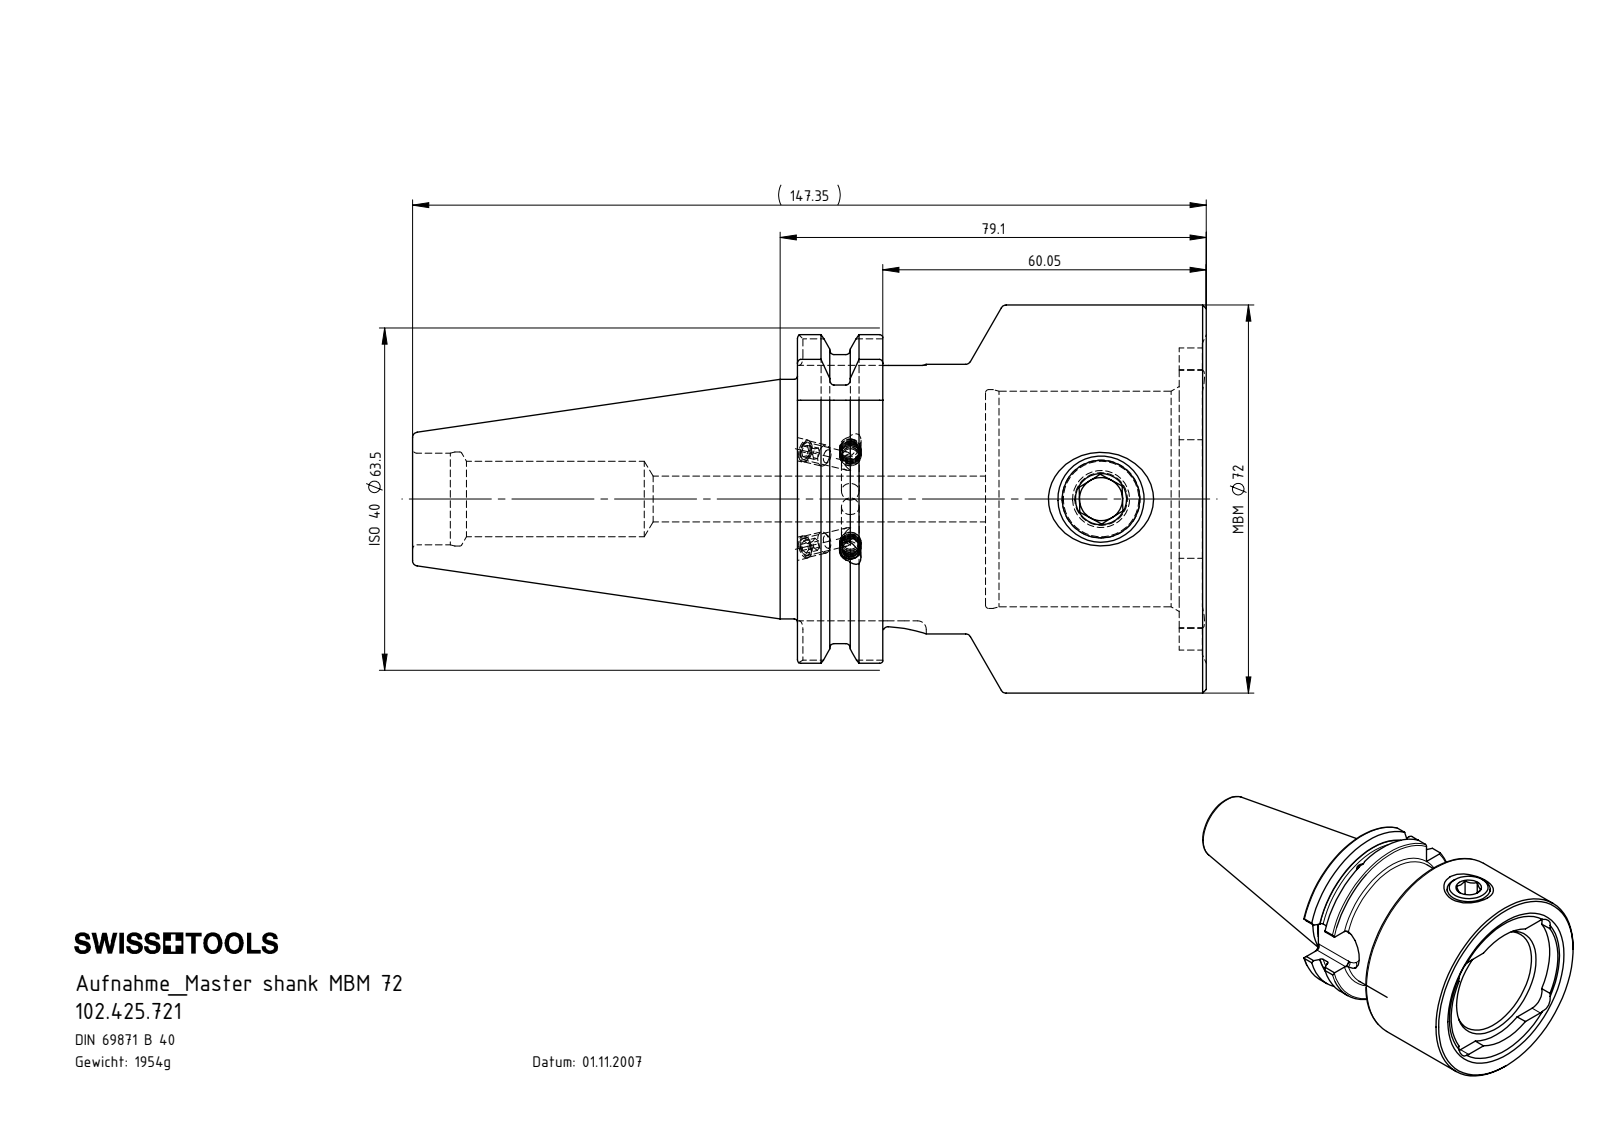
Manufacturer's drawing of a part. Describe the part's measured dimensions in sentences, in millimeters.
The part is named "102.425.721; KVT_MB_600_040; ISO 4026 - M4 x 5_PreviewCfg; MB7-ER1.001.022_A (+1 more)". Its 3-D file was written by "SolidWorks 2017 (CONFIG_CONTROL_DESIGN)". It is 8 solids with 322 faces: 81 planar, 96 cylindrical and 145 other. Overall it measures 147.35 by 72 by 72 millimeters. Its volume is 248 884 cubic millimeters and its surface area 43 756 square millimeters. Round holes: 3 of diameter 3.3, 2 of diameter 3, 2 of diameter 4.2, 1 of diameter 4, 1 of diameter 8, 1 of diameter 8.5, 1 of diameter 14, 1 of diameter 14.5, 1 of diameter 17, 1 of diameter 17.45, 1 of diameter 40, 1 of diameter 40.6. Round bosses or shafts: 4 of diameter 4, 1 of diameter 72, 1 of diameter 50, 1 of diameter 44.45, 1 of diameter 16. Partial cylindrical surfaces (rounded edges, fillets, slot ends): 8 of radius 1.6, 4 of radius 5.2, 1 of radius 8, 1 of radius 8.05, 1 of radius 23.75, 1 of radius 28, 1 of radius 28.02, 1 of radius 31.75. The main face-to-face distances are 34.9, 75.9, 41, 70.85, 35.95, 5.05, 15.85, 19.05, 55, 60.05.
